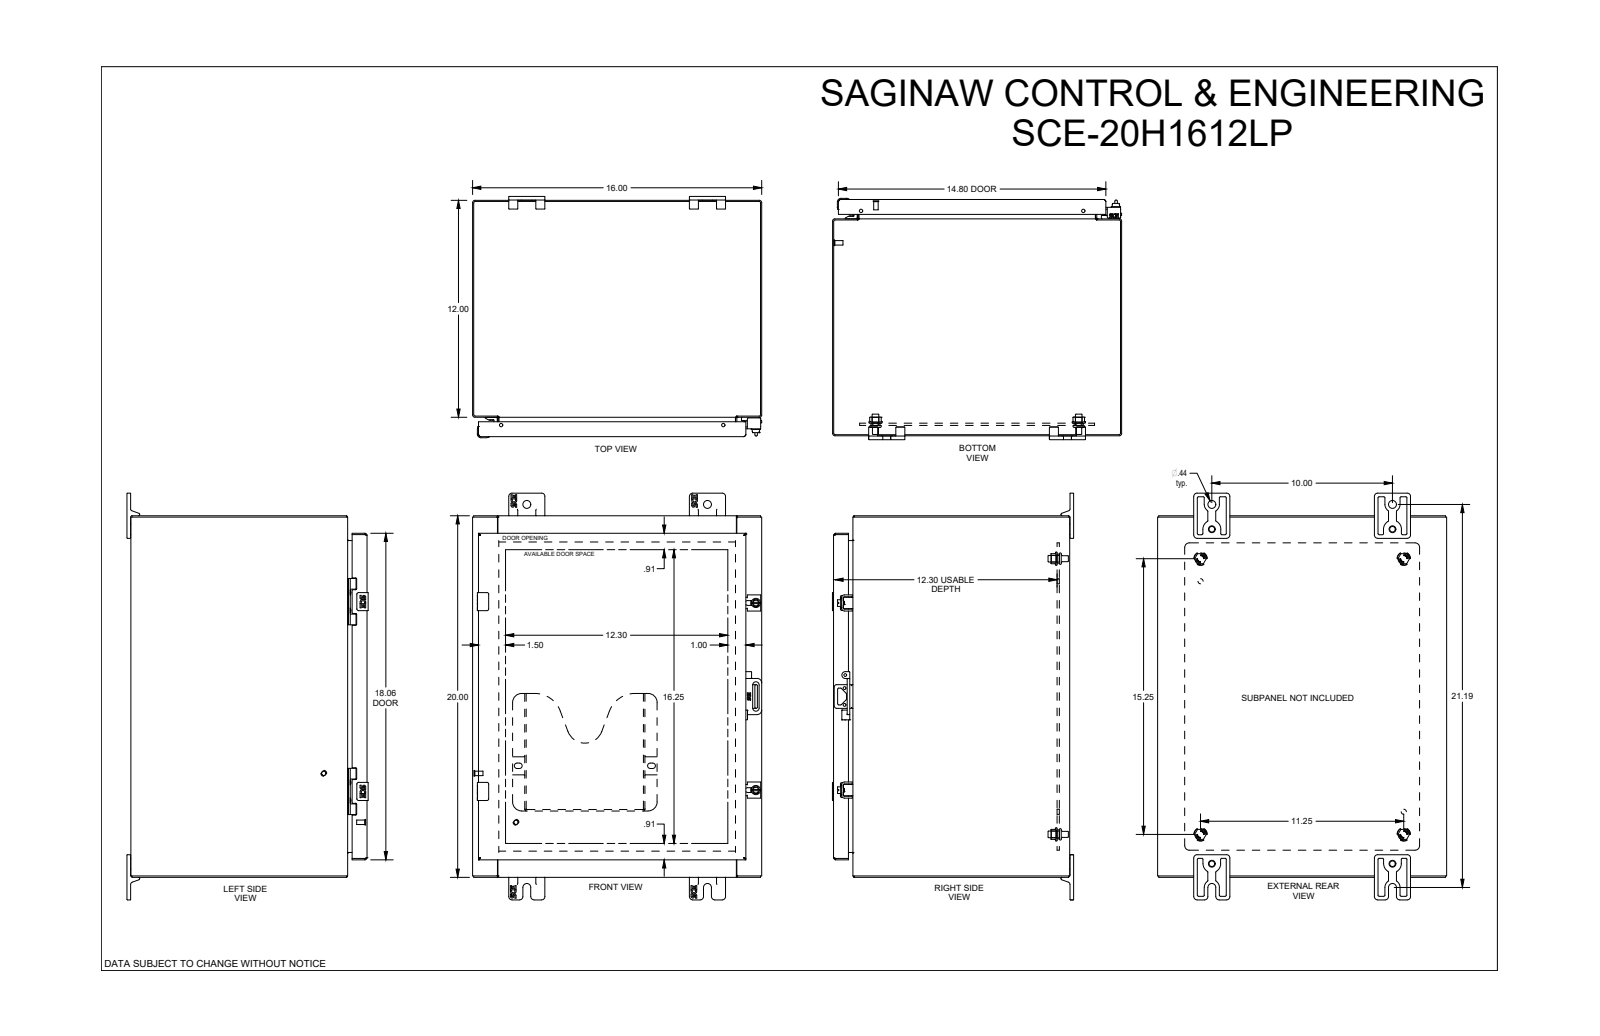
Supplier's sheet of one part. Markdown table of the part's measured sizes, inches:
| quantity | value |
| --- | --- |
| part name | SCE-20H1612LP |
| STEP written by | SolidWorks 2021 (AUTOMOTIVE_DESIGN) |
| units | inches |
| bodies | 38 solids, 2033 faces (790 planar, 853 cylindrical, 390 other) |
| overall size | 22.5 × 16 × 13.343 |
| volume | 168.2 in³ |
| surface area | 4 066 in² |
| round holes (diameter × count) | 0.172 × 4, 0.205 × 4, 0.218 × 4, 0.244 × 4, 0.312 × 4, 0.437 × 4, 0.5 × 4, 0.375 × 3, 0.04 × 2, 0.16 × 2, 0.188 × 2, 0.203 × 2 |
| round bosses / shafts (diameter × count) | 0.248 × 7, 0.25 × 6, 0.59 × 4, 0.376 × 4, 0.375 × 4, 0.33 × 4, 0.31 × 4, 0.24 × 4 |
| partial cylindrical surfaces (radius × count) | 0.025 × 68, 0.01 × 62, 0.03 × 32, 0.06 × 28, 0.015 × 24, 0.185 × 21, 0.04 × 18, 0.22 × 16 |
| main face-to-face distances | 0.075, 15.925, 19.925, 0.06, 12.993, 13.068, 13.008, 12.933, 16, 15.85 |
| hole center spacings | 16.887, 18.5, 1.375, 1.741, 1.741, 2.942, 4.916, 9.999 |
